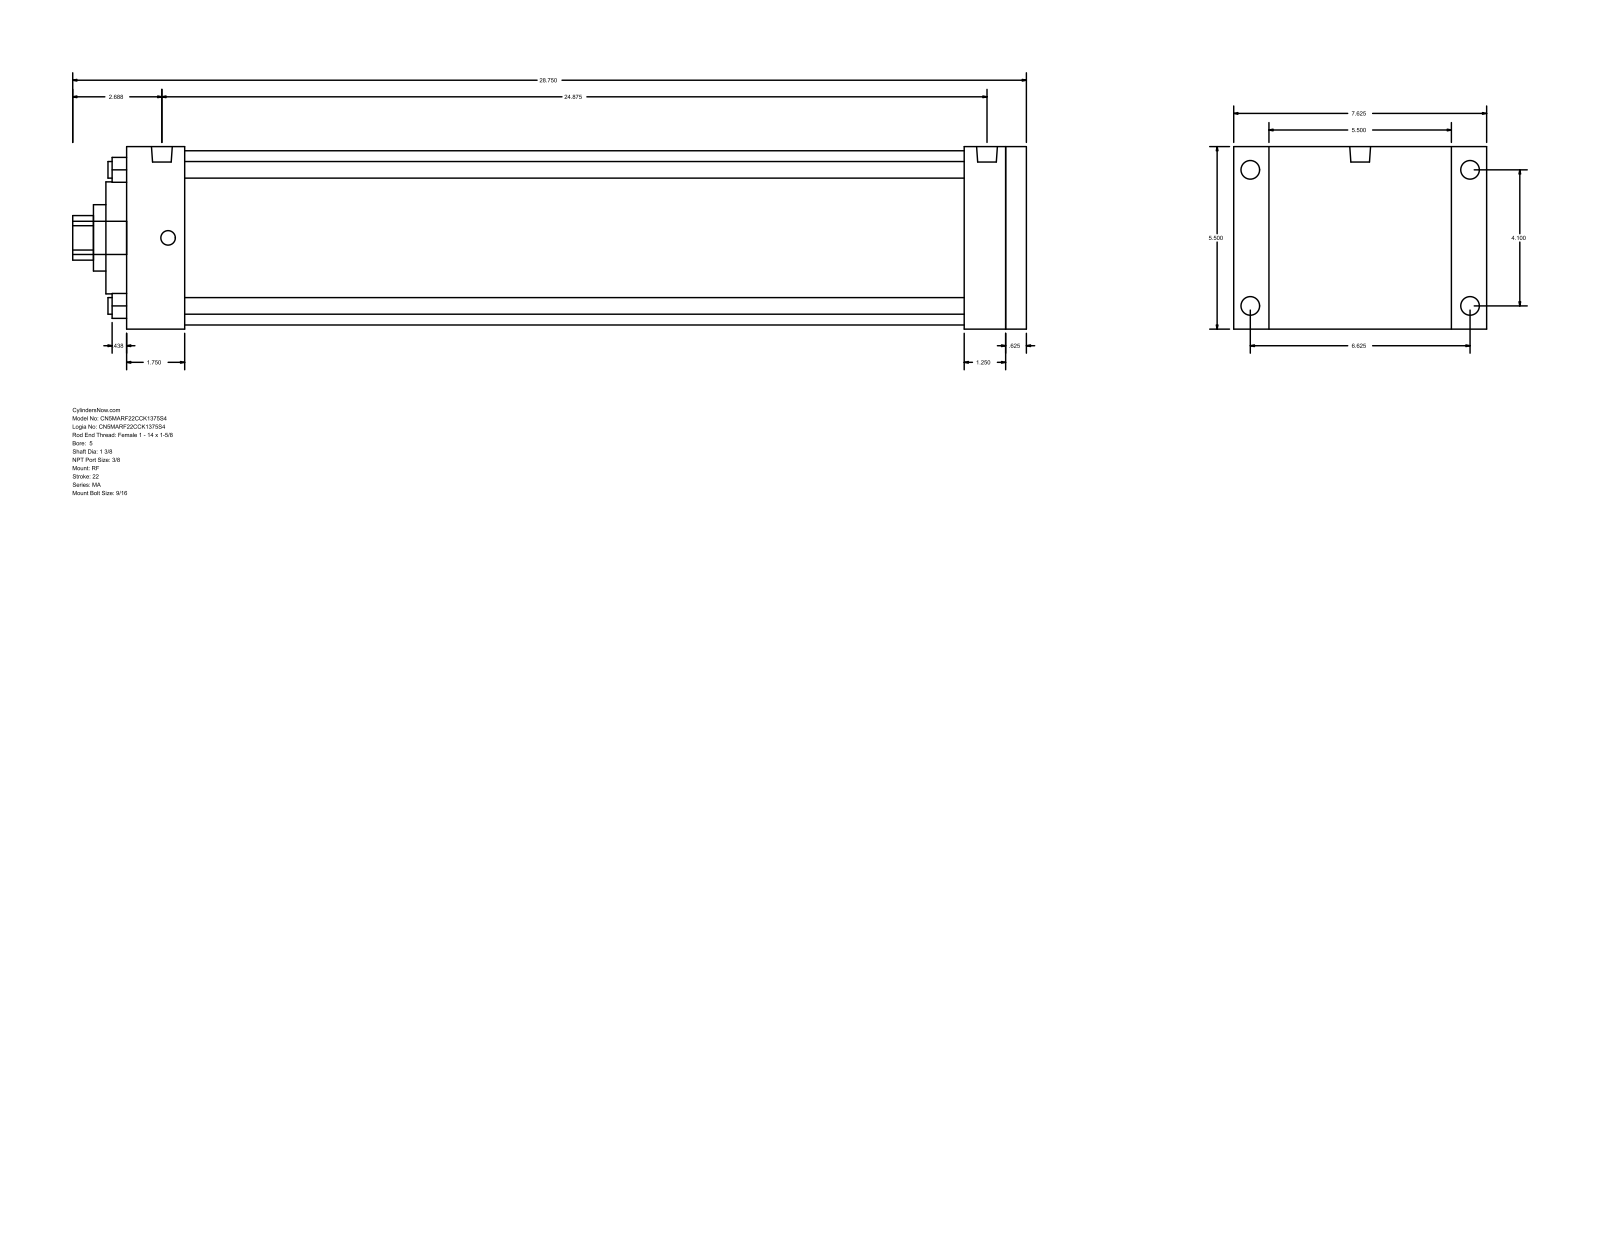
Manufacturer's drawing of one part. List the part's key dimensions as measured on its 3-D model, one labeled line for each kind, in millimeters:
Part name (STEP PRODUCT): MA_RF__0500_1.375
STEP written by: GSSL Pune (CONFIG_CONTROL_DESIGN)
Units: millimetres
Bodies: 0 solids, 94 faces (65 planar, 29 cylindrical, 0 other)
Overall size (bounding box): 730.25 × 193.68 × 139.7
Round holes (diameter × count): ⌀12.7 ×4, ⌀34.92 ×1, ⌀50.8 ×1, ⌀85.72 ×1, ⌀133.35 ×1
Round bosses / shafts (diameter × count): ⌀14.29 ×4, ⌀11.11 ×4, ⌀15.93 ×2, ⌀25.4 ×1
Partial cylindrical surfaces — rounded edges, fillets, slot ends (radius × count): R17.06 ×1
Main face-to-face distances: 139.7, 688.98, 15.87, 673.11, 44.45, 628.66, 644.53, 641.35, 596.9, 31.76
Hole centre spacings: 73.64, 104.14, 147.28
